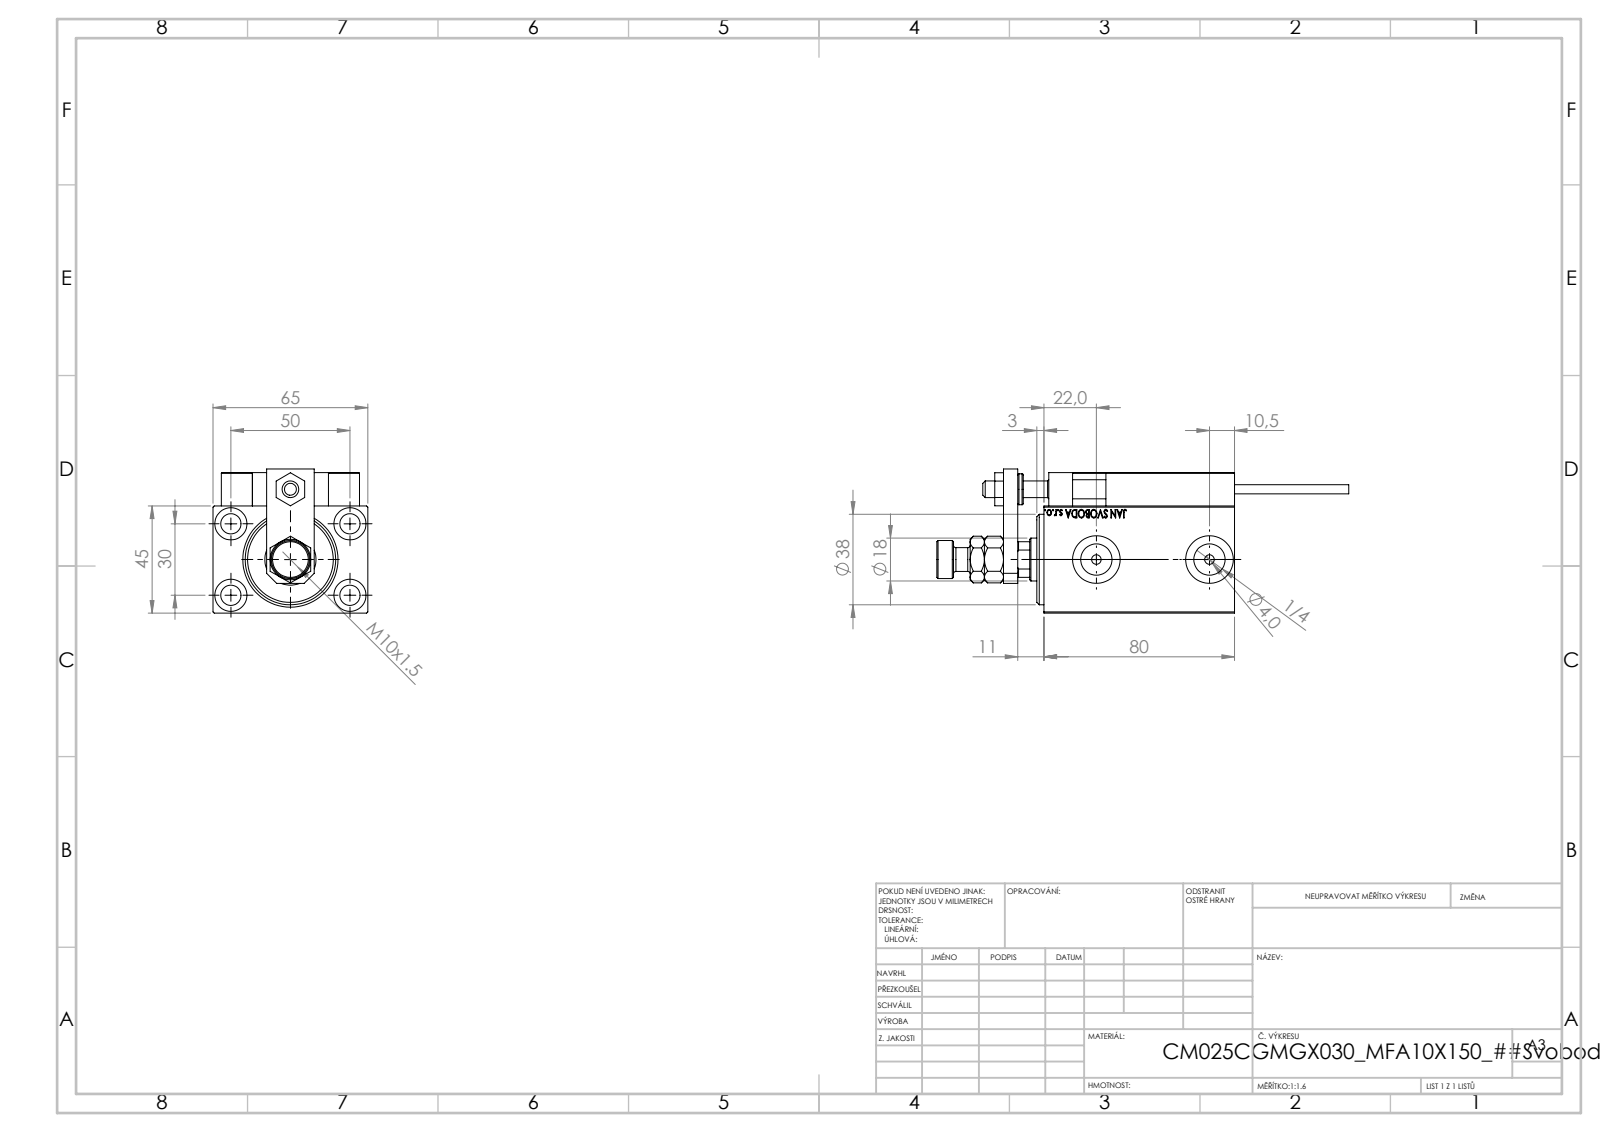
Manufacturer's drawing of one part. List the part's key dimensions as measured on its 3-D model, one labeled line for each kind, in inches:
Part name (STEP PRODUCT): V450CM_C_VCP; SWITCH DIM B,W; NUT_D12; TYC_L79 (+7 more)
STEP written by: SolidWorks 2019 (CONFIG_CONTROL_DESIGN)
Units: inches
Bodies: 24 solids, 1334 faces (576 planar, 192 cylindrical, 566 other)
Overall size (bounding box): 6.811 × 2.559 × 2.382
Volume: 15.47 in³ · Surface area: 118 in²
Round holes (diameter × count): ⌀0.157 ×6, ⌀0.315 ×5, ⌀0.335 ×5, ⌀0.126 ×4, ⌀0.531 ×4, ⌀0.197 ×2, ⌀0.518 ×2, ⌀0.787 ×2, ⌀0.276 ×1, ⌀0.571 ×1, ⌀0.709 ×1, ⌀0.846 ×1
Round bosses / shafts (diameter × count): ⌀0.197 ×2, ⌀0.15 ×2, ⌀0.63 ×1, ⌀0.512 ×1, ⌀0.433 ×1, ⌀0.394 ×1
Partial cylindrical surfaces — rounded edges, fillets, slot ends (radius × count): R0.012 ×30, R0.118 ×2, R0.335 ×1
Main face-to-face distances: 1.772, 0.551, 2.559, 2.323, 0.236, 0.118, 3.583, 0.197, 0.276, 2.717
Hole centre spacings: 1.148, 0.448, 0.787, 1.138, 1.165, 1.169, 1.181, 1.262
